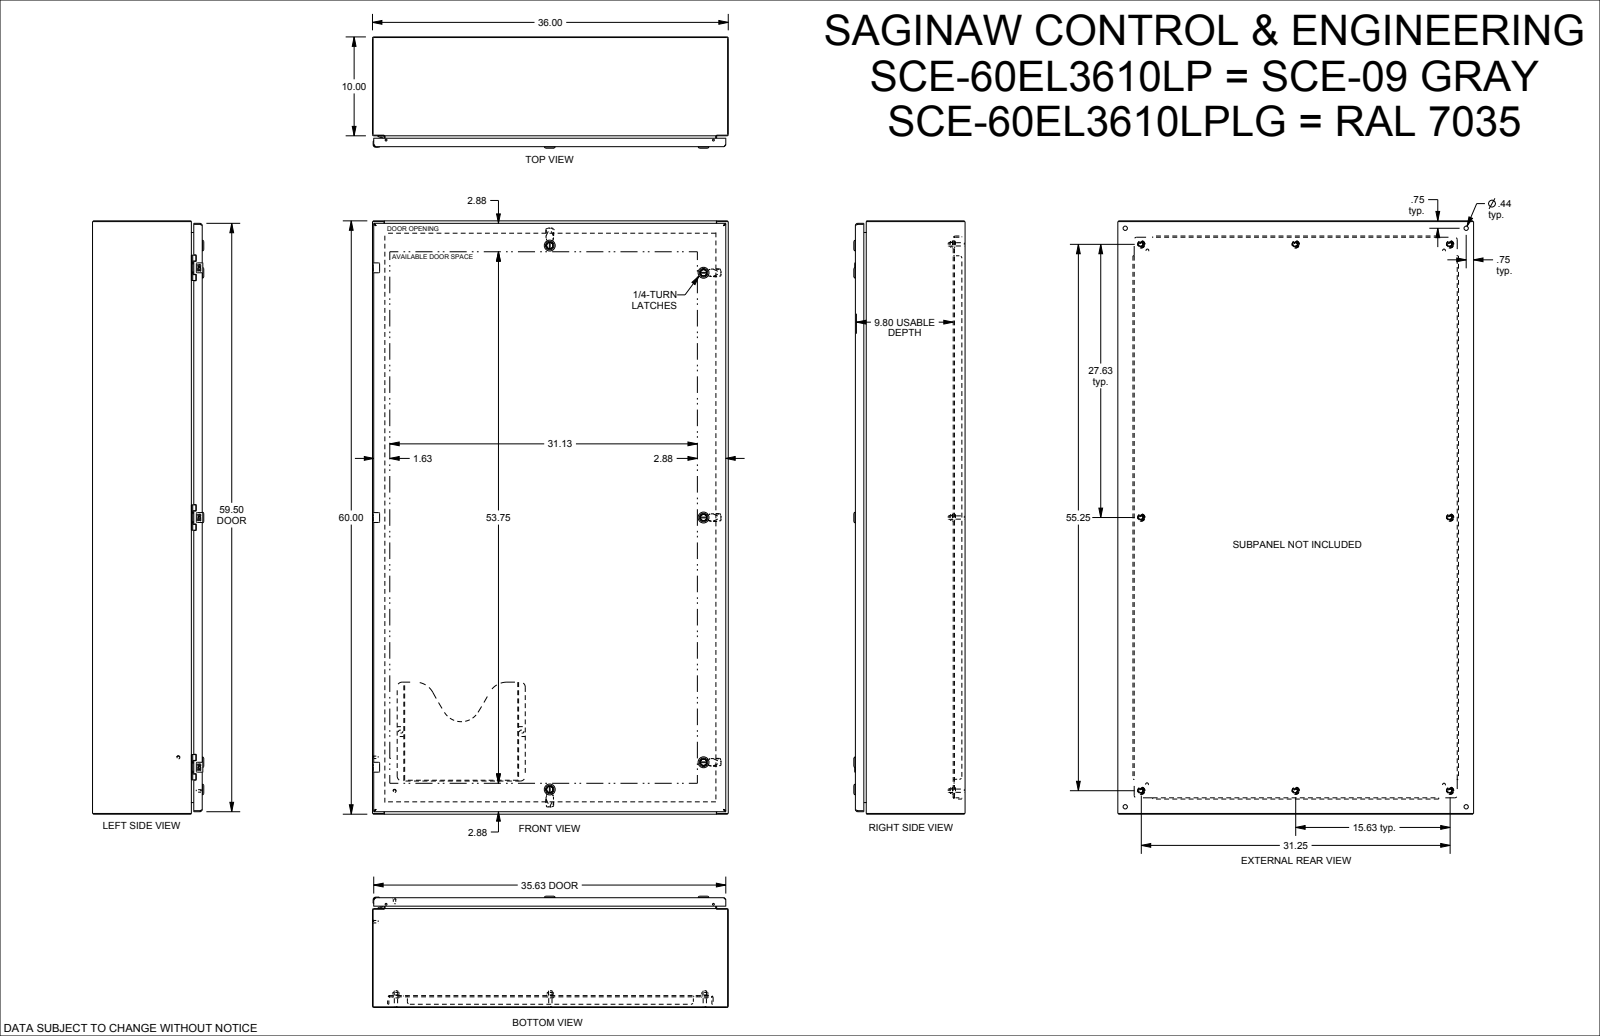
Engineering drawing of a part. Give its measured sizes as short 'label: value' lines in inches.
name: SCE-60EL3610LP_REV1
written by: SolidWorks 2021 (AUTOMOTIVE_DESIGN)
unit: in
bodies: 53 solids, 2286 faces (1129 planar, 772 cylindrical, 385 other)
size: 60 × 36 × 11.967
volume: 777.1 in³; area: 18 248 in²
holes: 8× ⌀0.5, 6× ⌀0.172, 6× ⌀0.205, 6× ⌀0.244, 6× ⌀0.375, 5× ⌀0.197, 5× ⌀0.394, 5× ⌀0.634, 4× ⌀0.281, 4× ⌀0.437, 3× ⌀0.04, 3× ⌀0.218
bosses: 8× ⌀0.375, 8× ⌀0.33, 7× ⌀0.17, 6× ⌀0.25, 6× ⌀0.24, 5× ⌀1.102, 5× ⌀0.78, 5× ⌀0.63
rounds: 28× R0.015, 20× R0.157, 17× R0.04, 16× R0.26, 14× R0.031, 12× R0.03, 12× R0.043, 12× R0.062
face distances: 0.075, 0.06, 11.097, 11.022, 11.037, 10.962, 1.125, 0.125, 1.075, 1
hole spacings: 25.25, 17.327, 2.298, 15.625, 27.625, 29.296, 31.738, 32.916
